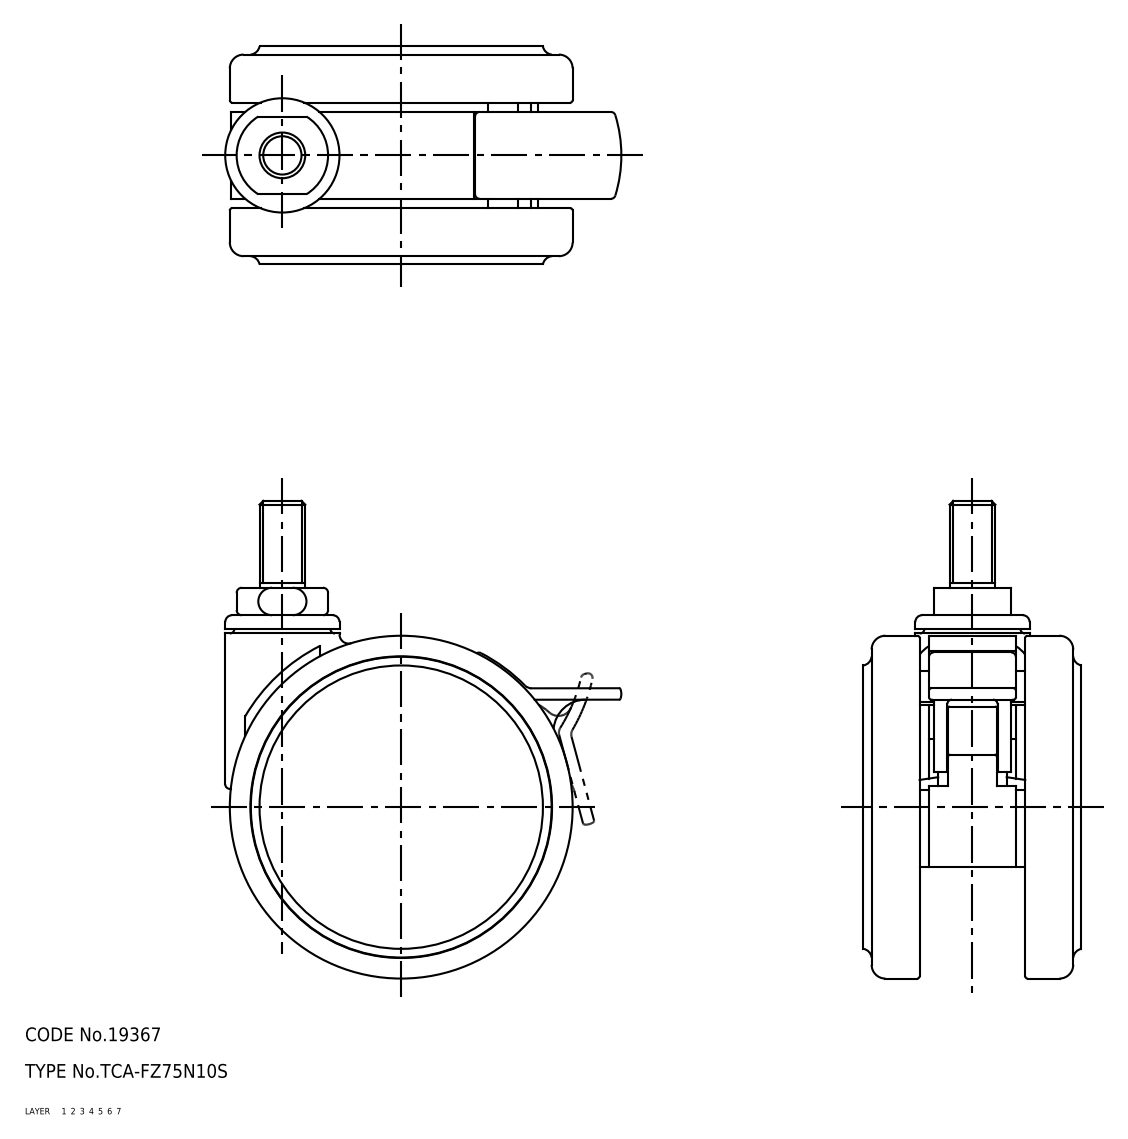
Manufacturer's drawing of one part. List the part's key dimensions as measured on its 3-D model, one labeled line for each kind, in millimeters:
Part name (STEP PRODUCT): caster; TCA-FZ75N10S
STEP written by: SolidWorks 2015 (AUTOMOTIVE_DESIGN)
Units: millimetres
Bodies: 1 solid, 2254 faces (508 planar, 984 cylindrical, 762 other)
Overall size (bounding box): 104.5 × 86.66 × 47.7
Volume: 119 073 mm³ · Surface area: 71 140 mm²
Round holes (diameter × count): ⌀2.4 ×1, ⌀3.6 ×1, ⌀5.8 ×1, ⌀6.5 ×1, ⌀8 ×1, ⌀8.1 ×1, ⌀8.5 ×1, ⌀9 ×1, ⌀10.2 ×1, ⌀11 ×1, ⌀16.2 ×1, ⌀17 ×1
Round bosses / shafts (diameter × count): ⌀16 ×2, ⌀65.8 ×1, ⌀54 ×1, ⌀26 ×1, ⌀25 ×1, ⌀14 ×1, ⌀10 ×1, ⌀8.1 ×1
Partial cylindrical surfaces — rounded edges, fillets, slot ends (radius × count): R1 ×176, R0.5 ×158, R0.3 ×142, R0.2 ×18, R2 ×13, R1.5 ×7, R0.7 ×2, R0.8 ×2
Main face-to-face distances: 1.5, 46.2, 1.8, 3.3, 44.4, 42.9, 32.1, 9, 12.3, 35.4
Hole centre spacings: 30
